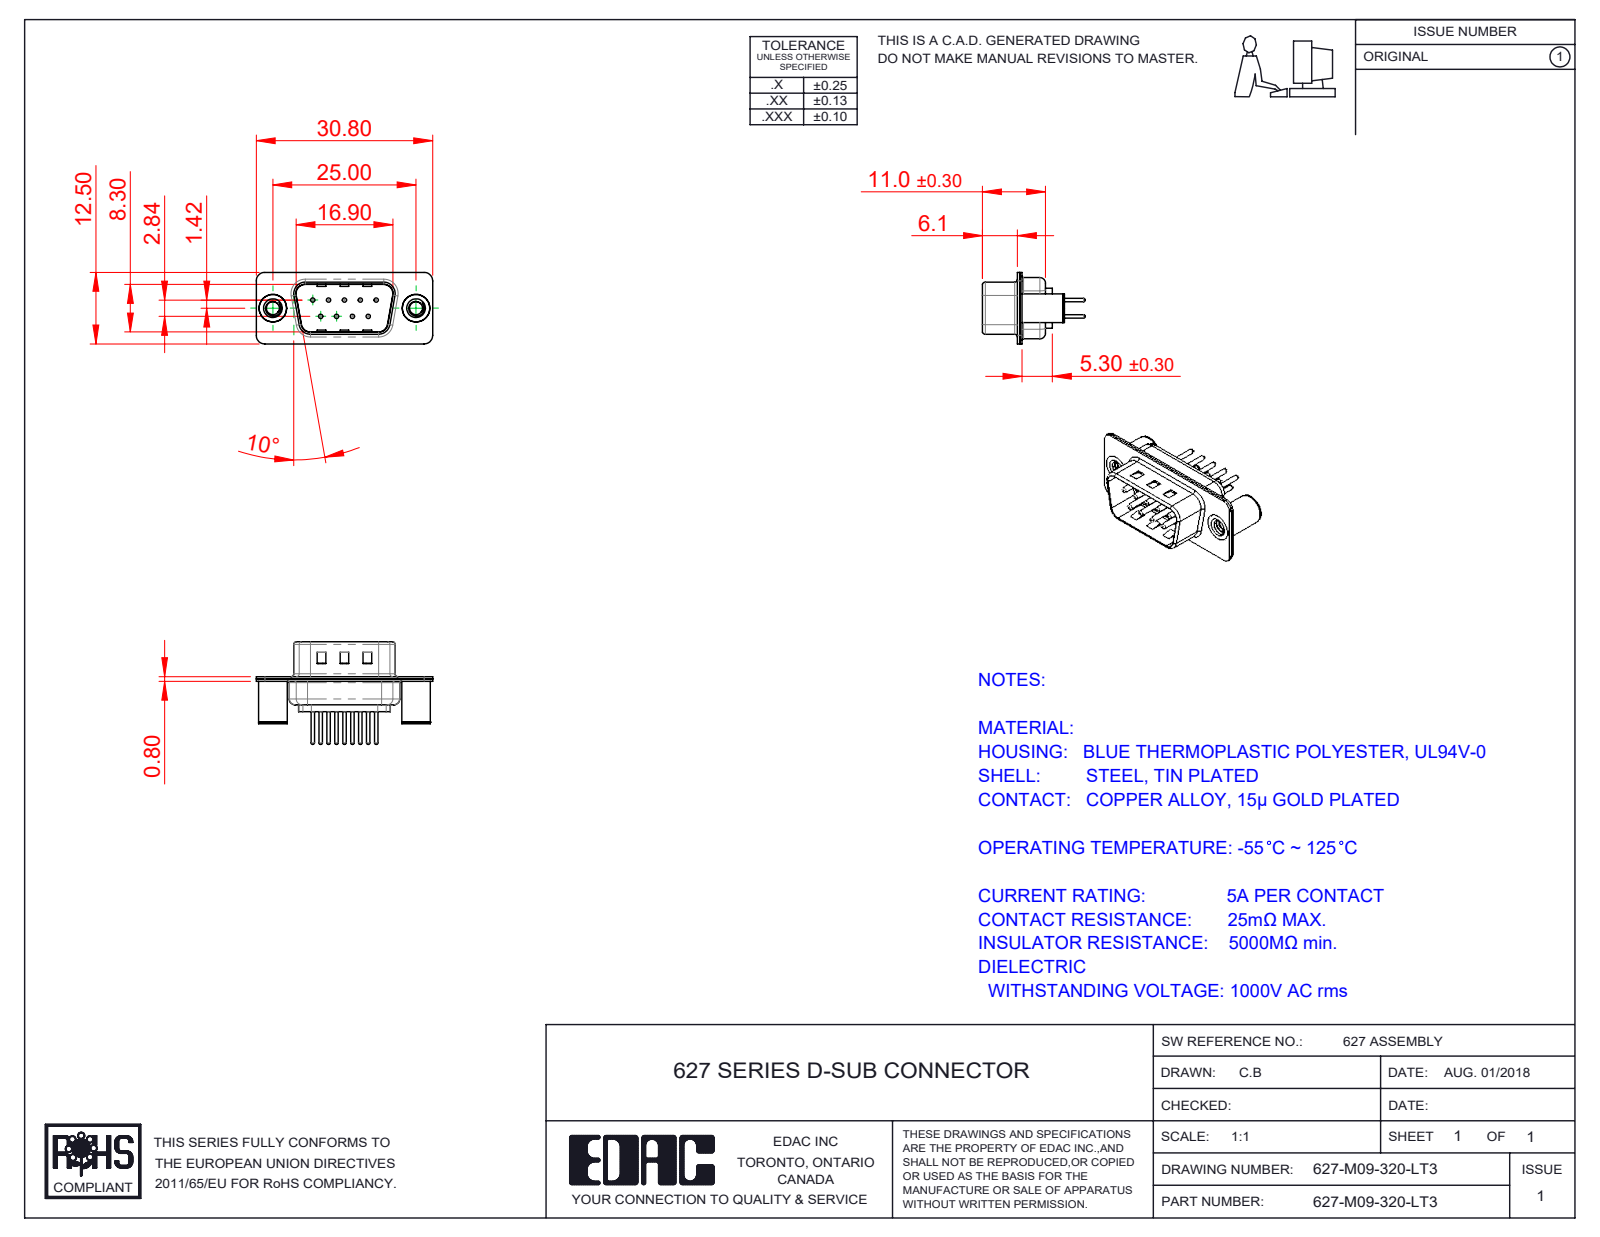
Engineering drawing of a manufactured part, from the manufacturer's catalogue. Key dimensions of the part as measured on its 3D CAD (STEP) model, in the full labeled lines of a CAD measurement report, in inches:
Part name (STEP PRODUCT): 627-M09-320-LT3; 627M Shell Rear_09 Contacts; 627M Housing_09 Contacts; 627M Contact Row 1_20 (+3 more)
STEP written by: SolidWorks 2020 (CONFIG_CONTROL_DESIGN)
Units: inches
Bodies: 14 solids, 671 faces (170 planar, 279 cylindrical, 222 other)
Overall size (bounding box): 1.213 × 0.705 × 0.492
Volume: 0.087 in³ · Surface area: 5.94 in²
Round holes (diameter × count): ⌀0.03 ×9, ⌀0.063 ×9, ⌀0.079 ×9, ⌀0.089 ×2, ⌀0.128 ×2, ⌀0.157 ×2, ⌀0.189 ×2
Round bosses / shafts (diameter × count): ⌀0.059 ×9, ⌀0.024 ×9, ⌀0.197 ×2, ⌀0.193 ×2
Partial cylindrical surfaces — rounded edges, fillets, slot ends (radius × count): R0.059 ×16, R0.079 ×12, R0.02 ×8, R0.063 ×8, R0.01 ×4, R0.024 ×4, R0.026 ×4, R0.035 ×4
Main face-to-face distances: 0.016, 0.031, 0.374, 0.358, 0.343, 0.026, 0.39, 0.047, 0.209, 0.24
Hole centre spacings: 0.124, 0.109, 0.218, 0.198, 0.198, 0.327, 0.28, 0.294
